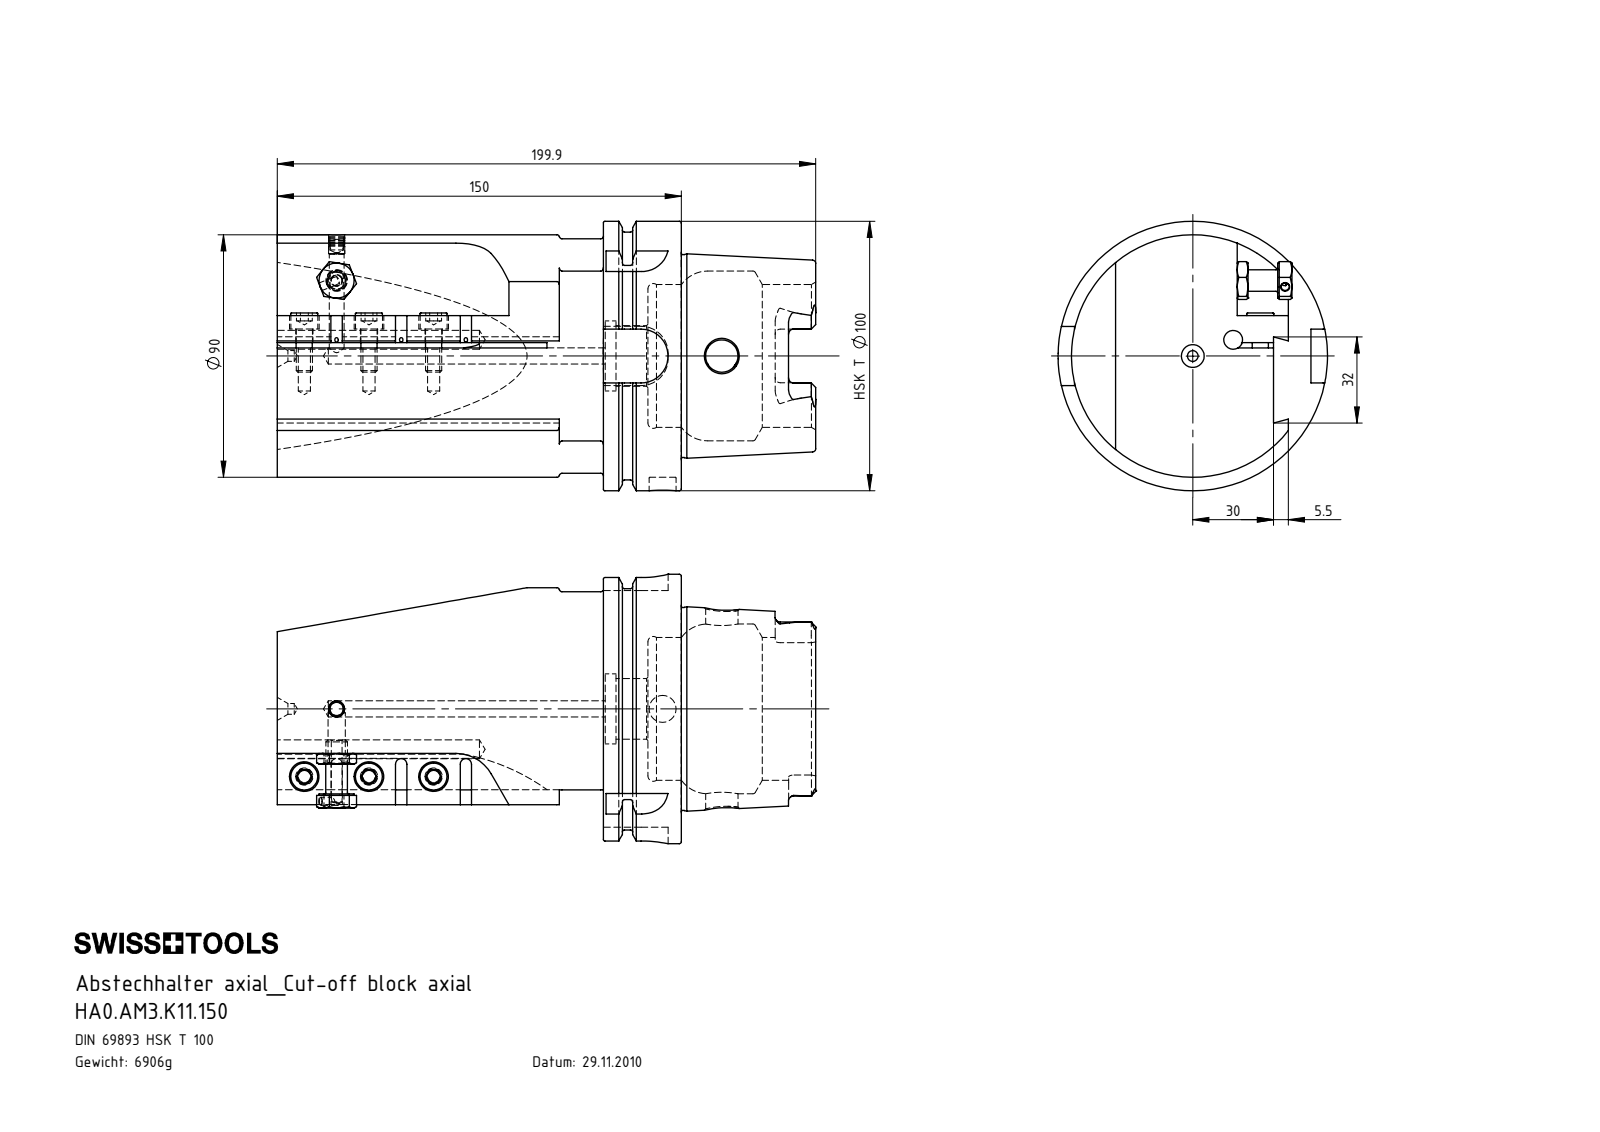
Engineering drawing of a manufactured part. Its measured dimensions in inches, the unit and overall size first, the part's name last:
Units: inches
Overall size (bounding box): 7.87 × 3.937 × 3.937
Round holes (diameter × count): ⌀0.252 ×4, ⌀0.177 ×3, ⌀0.433 ×3, ⌀0.157 ×2, ⌀0.276 ×2, ⌀0.118 ×1, ⌀0.197 ×1, ⌀0.217 ×1, ⌀0.236 ×1, ⌀0.394 ×1, ⌀0.472 ×1, ⌀0.886 ×1
Round bosses / shafts (diameter × count): ⌀0.236 ×4, ⌀0.394 ×3, ⌀3.937 ×1, ⌀3.62 ×1, ⌀2.965 ×1, ⌀0.512 ×1, ⌀0.315 ×1
Partial cylindrical surfaces — rounded edges, fillets, slot ends (radius × count): R0.075 ×6, R0.394 ×4, R0.039 ×3, R0.083 ×3, R0.192 ×2, R0.194 ×2, R0.591 ×1, R1.713 ×1
Main face-to-face distances: 5.906, 1.14, 4.766, 0.531, 0.49, 0.65, 5.415, 0.748, 0.217, 0.197
Hole centre spacings: 0.945, 1.095, 0.636, 1.728, 1.89, 3.489, 4.404, 4.764
Volume: 53.75 in³ · Surface area: 150.8 in²
Bodies: 8 solids, 423 faces (144 planar, 117 cylindrical, 162 other)
Part name (STEP PRODUCT): HA0.AM3.K11.150; KVT_MB_600_060; ISO 4035 - M8_PreviewCfg; AM3-ER1.001.020_PreviewCfg (+2 more)
STEP written by: SolidWorks 2011 (AUTOMOTIVE_DESIGN)
